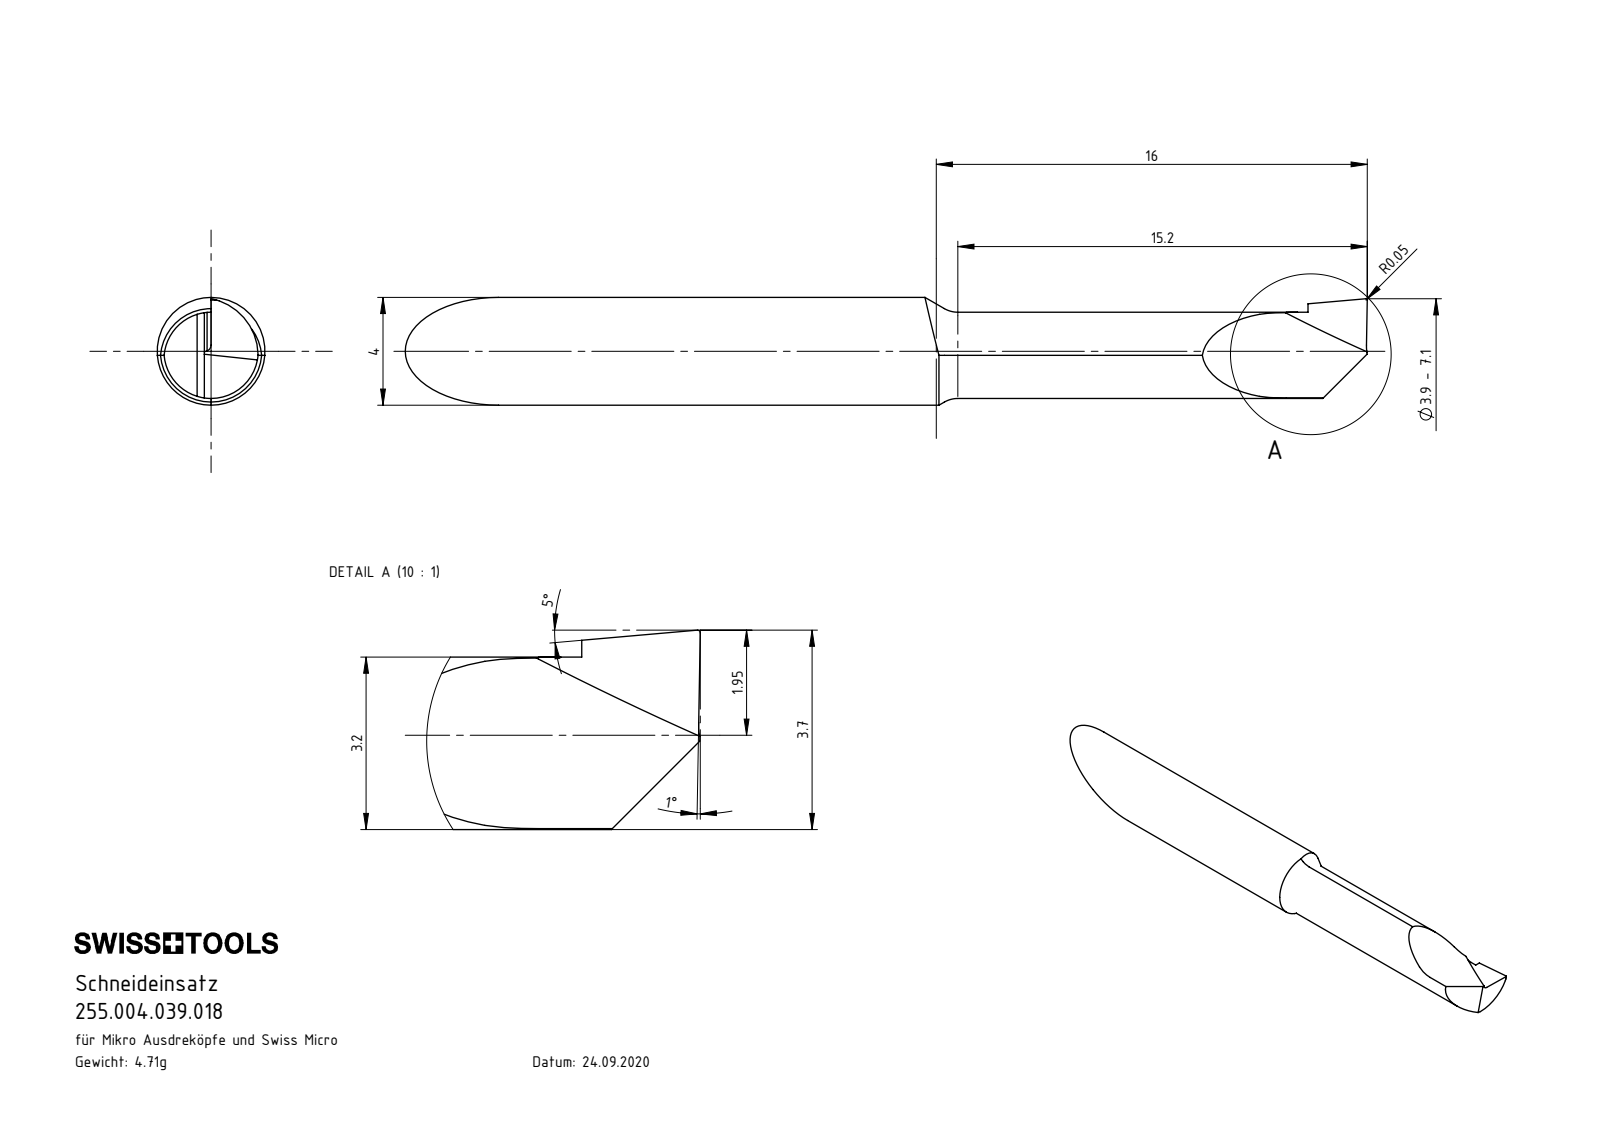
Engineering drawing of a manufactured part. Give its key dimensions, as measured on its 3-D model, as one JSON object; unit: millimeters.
{"part_name": "A04.0195.15.39.05_YR", "step_written_by": "SolidWorks 2017 (AUTOMOTIVE_DESIGN)", "units": "millimeters", "bodies": {"solids": 1, "faces": 27, "planar": 8, "cylindrical": 6, "other": 13}, "overall_size": [35.71, 4, 4], "volume_mm3": 325, "surface_area_mm2": 394, "round_bosses_or_shafts": [[4, 1]], "partial_cylinders_radius": [[1.75, 2], [2, 1]], "face_to_face_distances": [14.58]}
